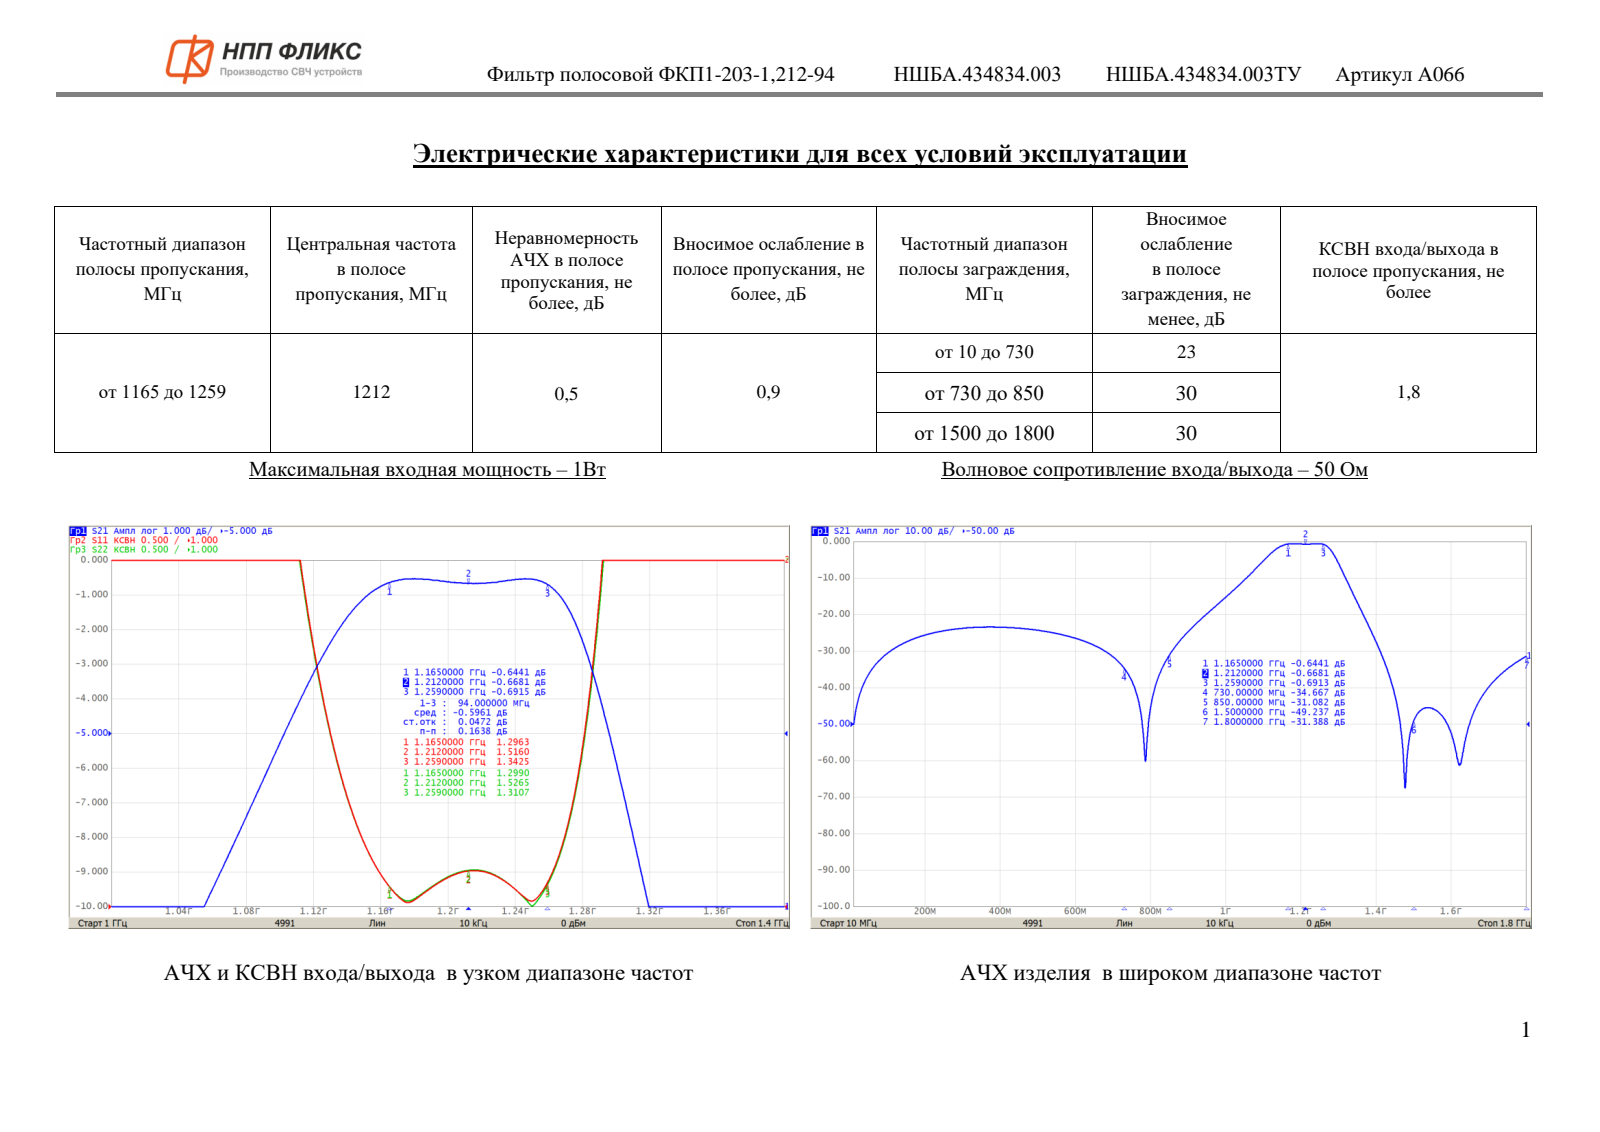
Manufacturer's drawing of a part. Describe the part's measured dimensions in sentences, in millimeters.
The part is named "НШБА.434834.003_Фильтр ФКП1-203-1,212-94". Its 3-D file was written by "ASCON Math Kernel (CONFIG_CONTROL_DESIGN)". It is 1 solid with 332 faces: 229 planar, 6 cylindrical and 97 other. Overall it measures 8.2 by 7 by 3.6 millimeters. Its volume is 207 cubic millimeters and its surface area 224 square millimeters. Partial cylindrical surfaces (rounded edges, fillets, slot ends): 3 of radius 0.15, 1 of radius 0.23, 1 of radius 0.26. The main face-to-face distances are 3.6, 7, 8.2, 2.6, 1.8, 3, 1.5, 0.8, 5.6, 1.35.
